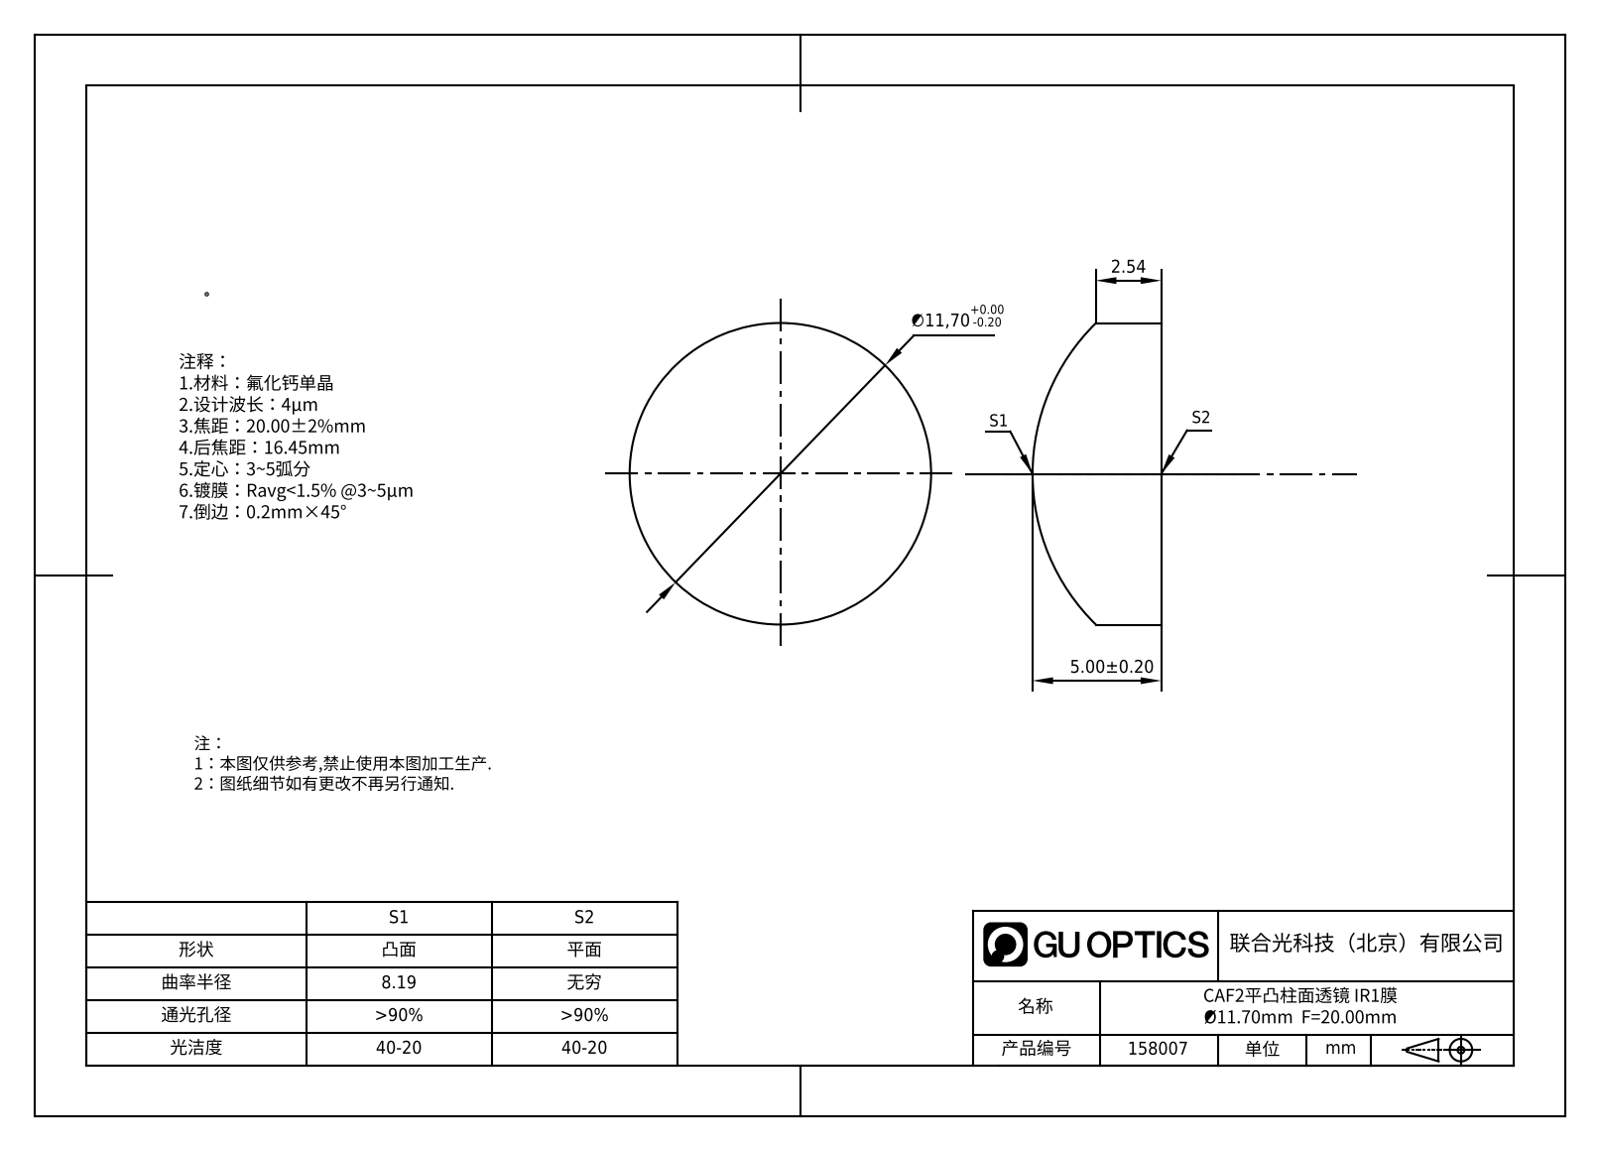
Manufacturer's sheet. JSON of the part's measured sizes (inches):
{"part_name": "GL55-012-020-IR1", "step_written_by": "SolidWorks 2022 (AUTOMOTIVE_DESIGN)", "units": "inches", "bodies": {"solids": 1, "faces": 9, "planar": 1, "cylindrical": 4, "other": 4}, "overall_size": [0.461, 0.461, 0.197], "volume_in3": 0.029, "surface_area_in2": 0.555, "round_bosses_or_shafts": [[0.461, 1]], "partial_cylinders_radius": [[0.322, 1]]}
